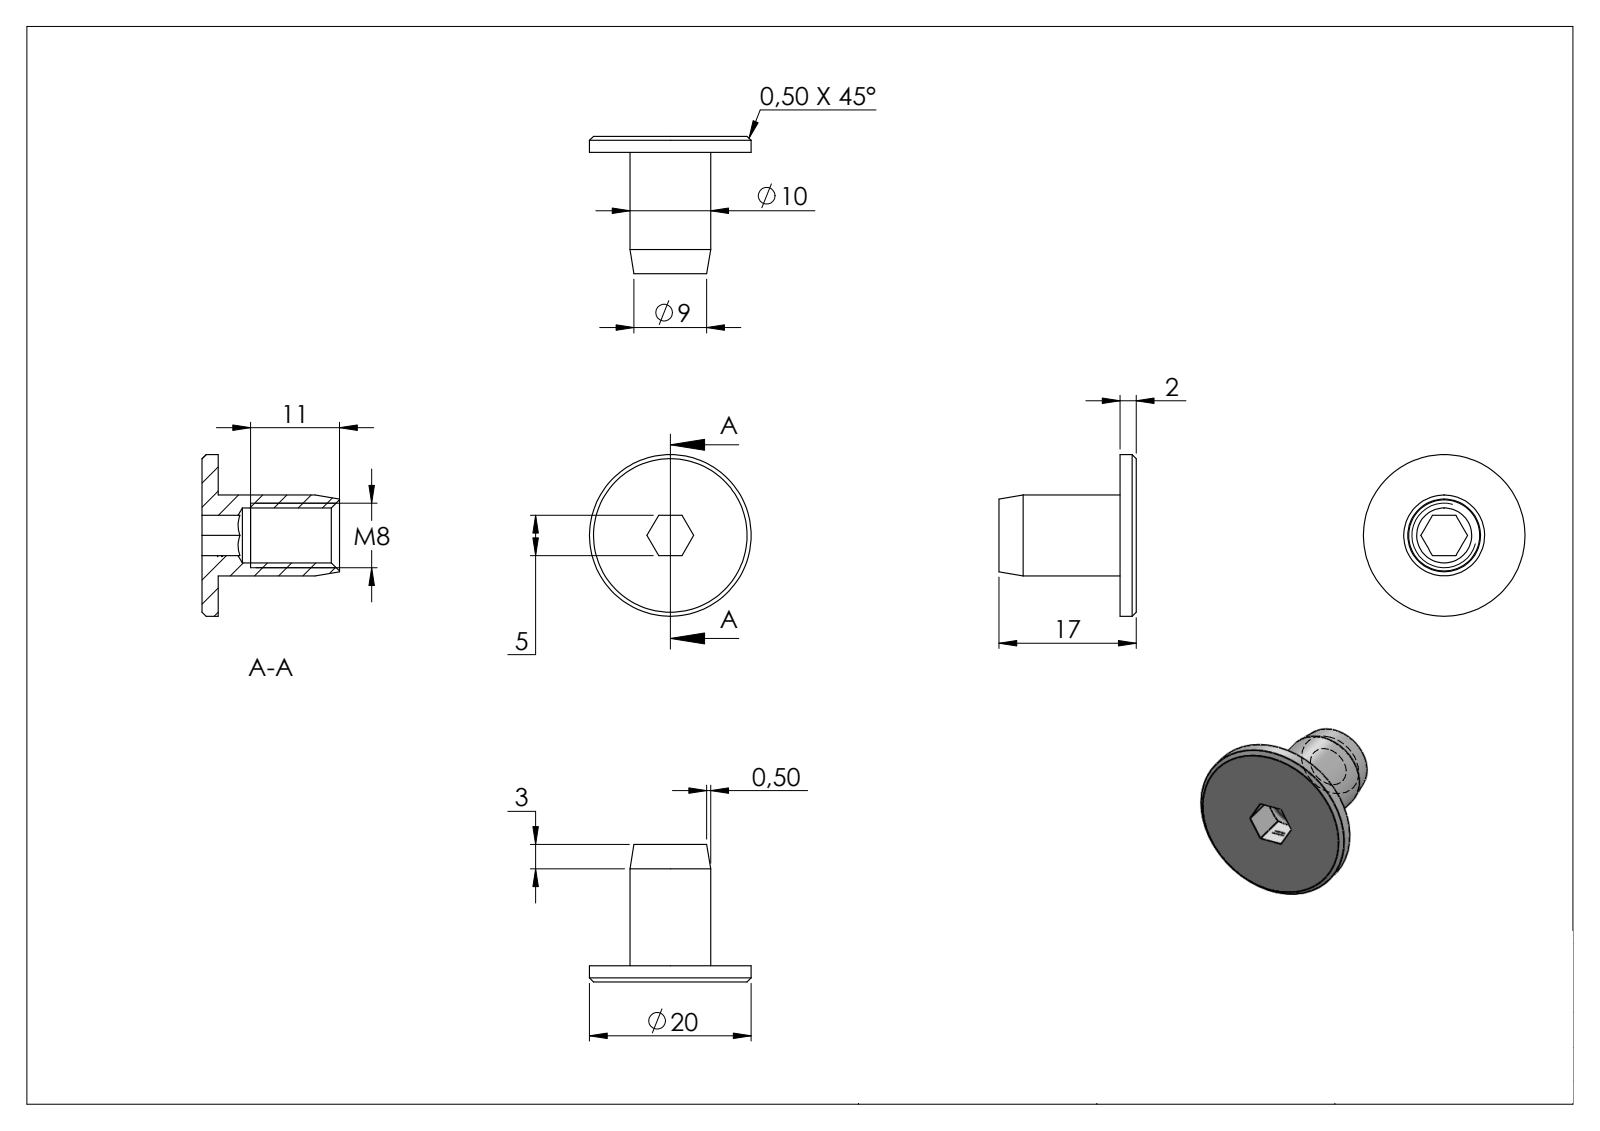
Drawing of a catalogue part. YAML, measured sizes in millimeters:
part_name: "58383-240-8"
step_written_by: "SolidWorks 2015 (CONFIG_CONTROL_DESIGN)"
units: millimeters
bodies: {solids: 1, faces: 296, planar: 132, cylindrical: 6, other: 158}
overall_size: [20, 20, 17]
volume: 1217
surface_area: 1473
round_holes:
  - {diameter: 6.8, count: 1}
round_bosses_or_shafts:
  - {diameter: 20, count: 1}
  - {diameter: 10, count: 1}
face_to_face_distances: [2, 5, 15, 17, 5.1, 0.5, 0.44, 0.46, 0.48, 0.53]
